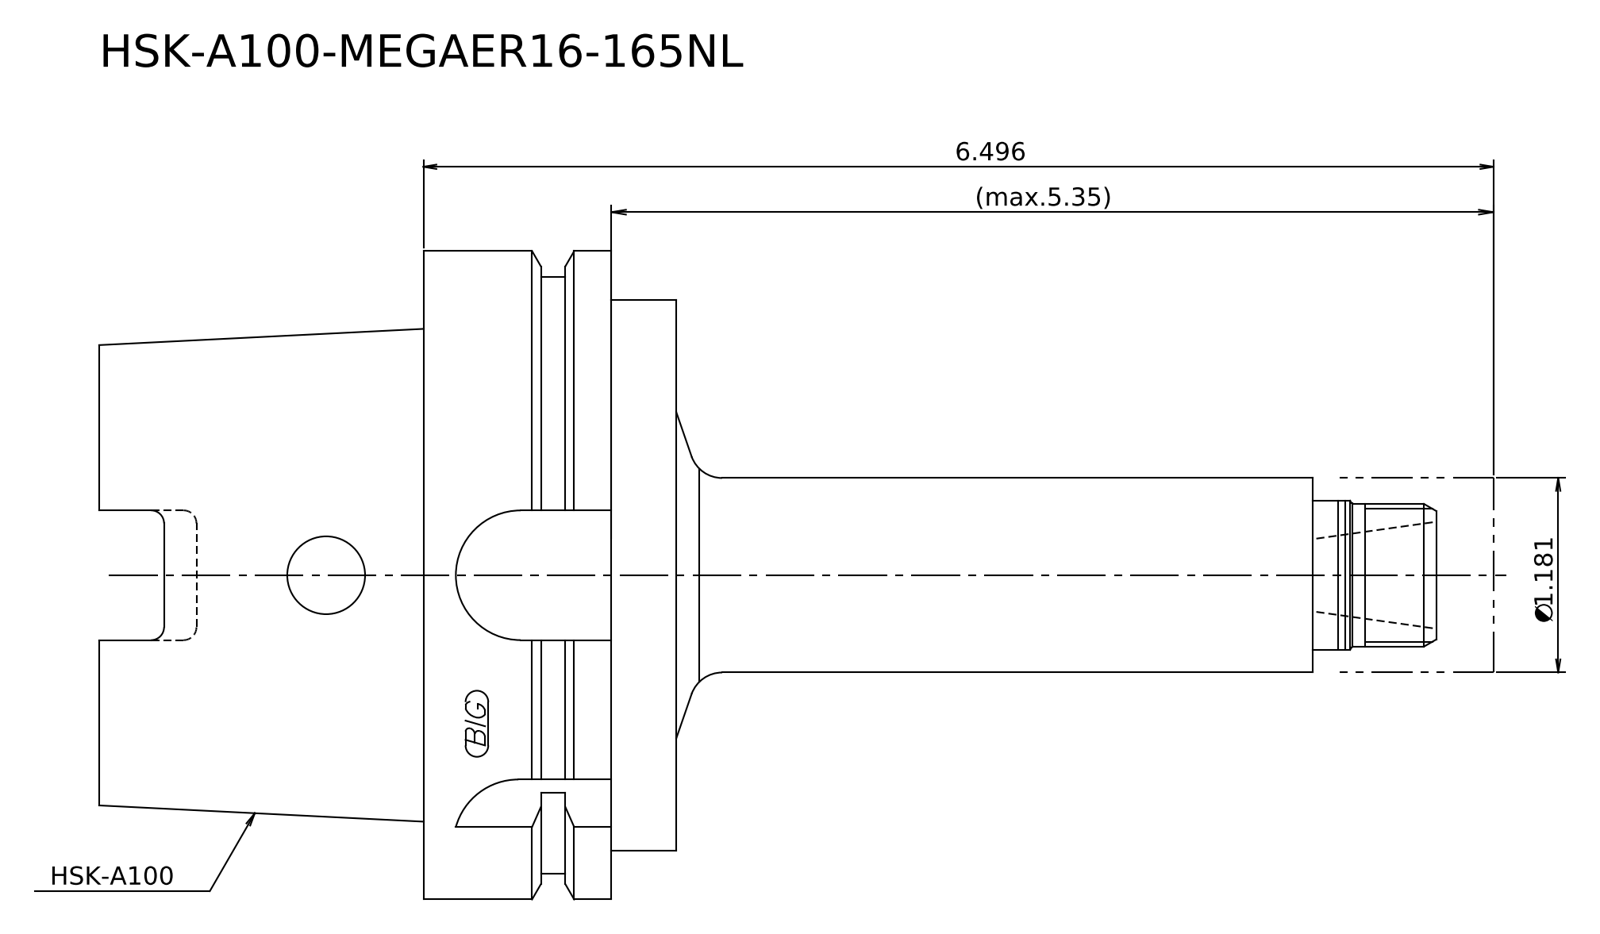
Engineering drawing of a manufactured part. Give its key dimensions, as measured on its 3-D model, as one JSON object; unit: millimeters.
{"step_written_by": "Kubotek KeyCreator 2011 V10.0.2 (22737) (automotive_design)", "units": "millimeters", "bodies": {"solids": 2, "faces": 24, "planar": 10, "cylindrical": 8, "other": 6}, "overall_size": [215, 100, 100], "volume_mm3": 589763, "surface_area_mm2": 54041, "round_bosses_or_shafts": [[100, 1], [92, 1], [85, 1], [30, 1], [23, 1], [22, 1]], "face_to_face_distances": [89, 39, 50, 10, 29, 79, 101, 111, 140, 190]}
